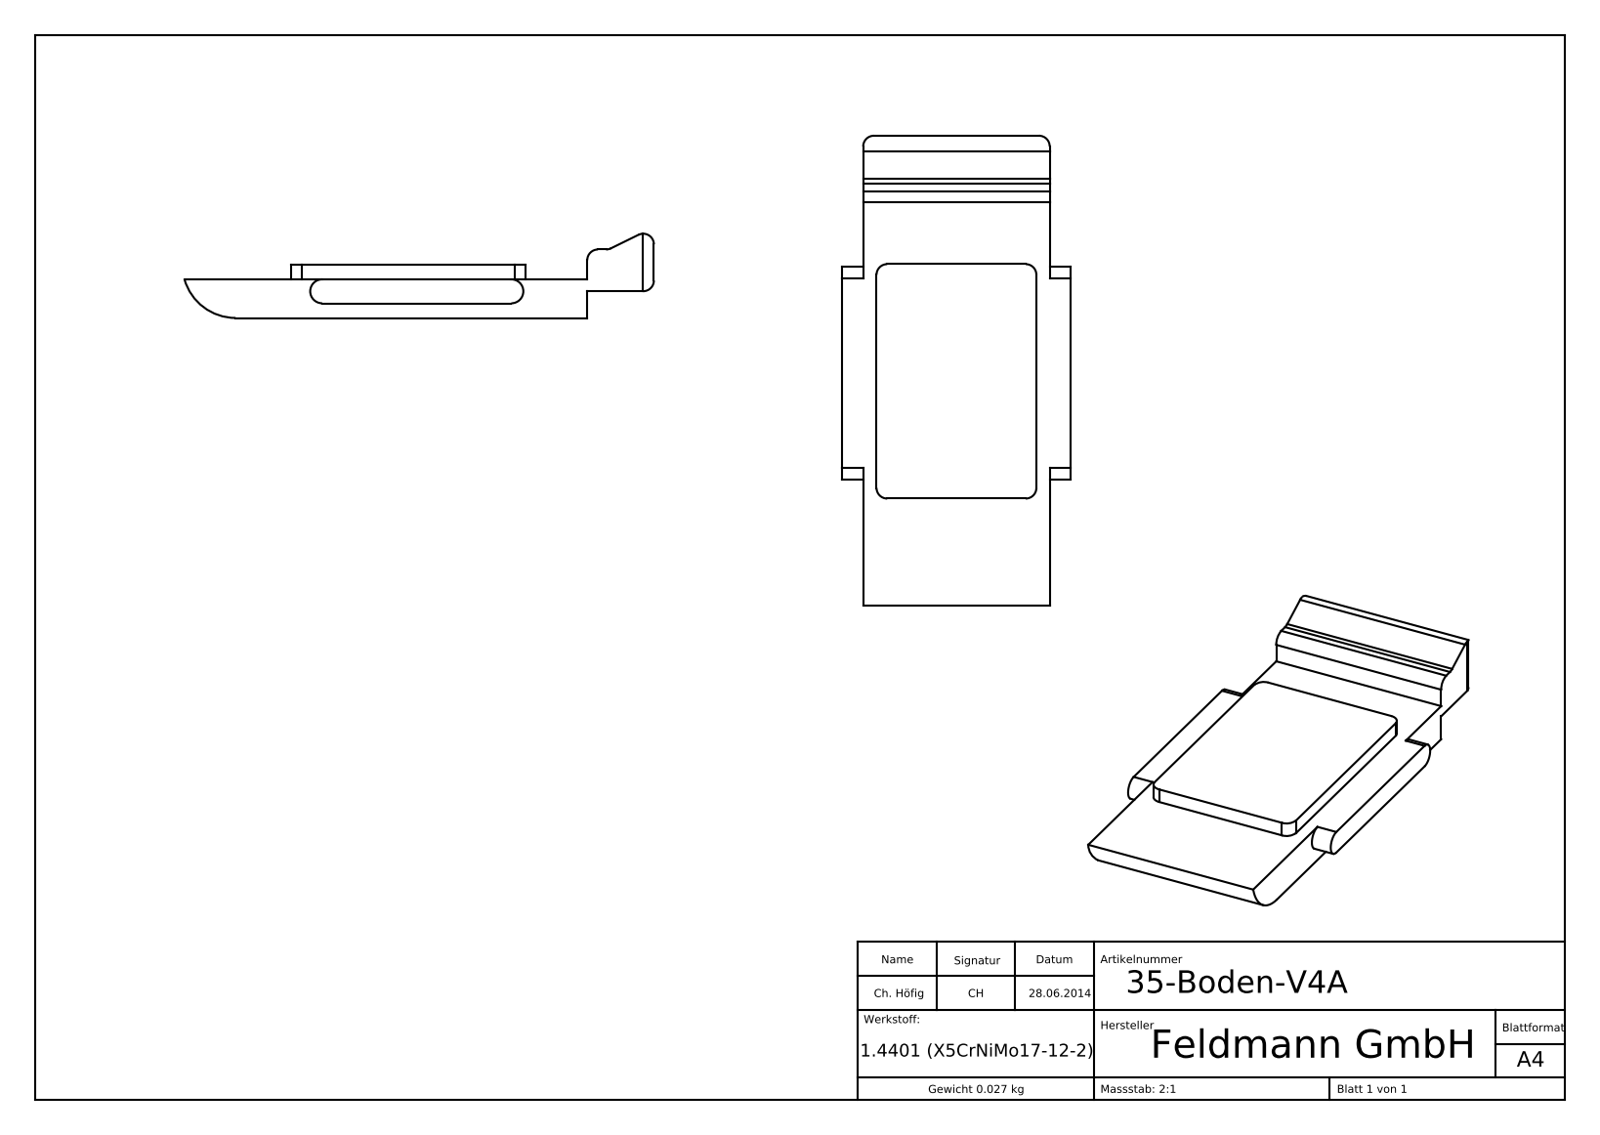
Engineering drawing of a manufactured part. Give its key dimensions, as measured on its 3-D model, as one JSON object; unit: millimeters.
{"part_name": "35-BODEN-V4A; 35-Boden-GU; 35-Boden; 35-Boden-GU_35-Boden-GU (+1 more)", "step_written_by": "SolidWorks 2018 (CONFIG_CONTROL_DESIGN)", "units": "millimeters", "bodies": {"solids": 2, "faces": 325, "planar": 182, "cylindrical": 23, "other": 120}, "overall_size": [44.25, 21.4, 7.83], "volume_mm3": 3412, "surface_area_mm2": 2888, "partial_cylinders_radius": [[1, 14], [5, 9]], "face_to_face_distances": [0.5, 4, 5, 1, 4.5, 17.4, 0.37, 3.63, 0.87, 1.37]}
